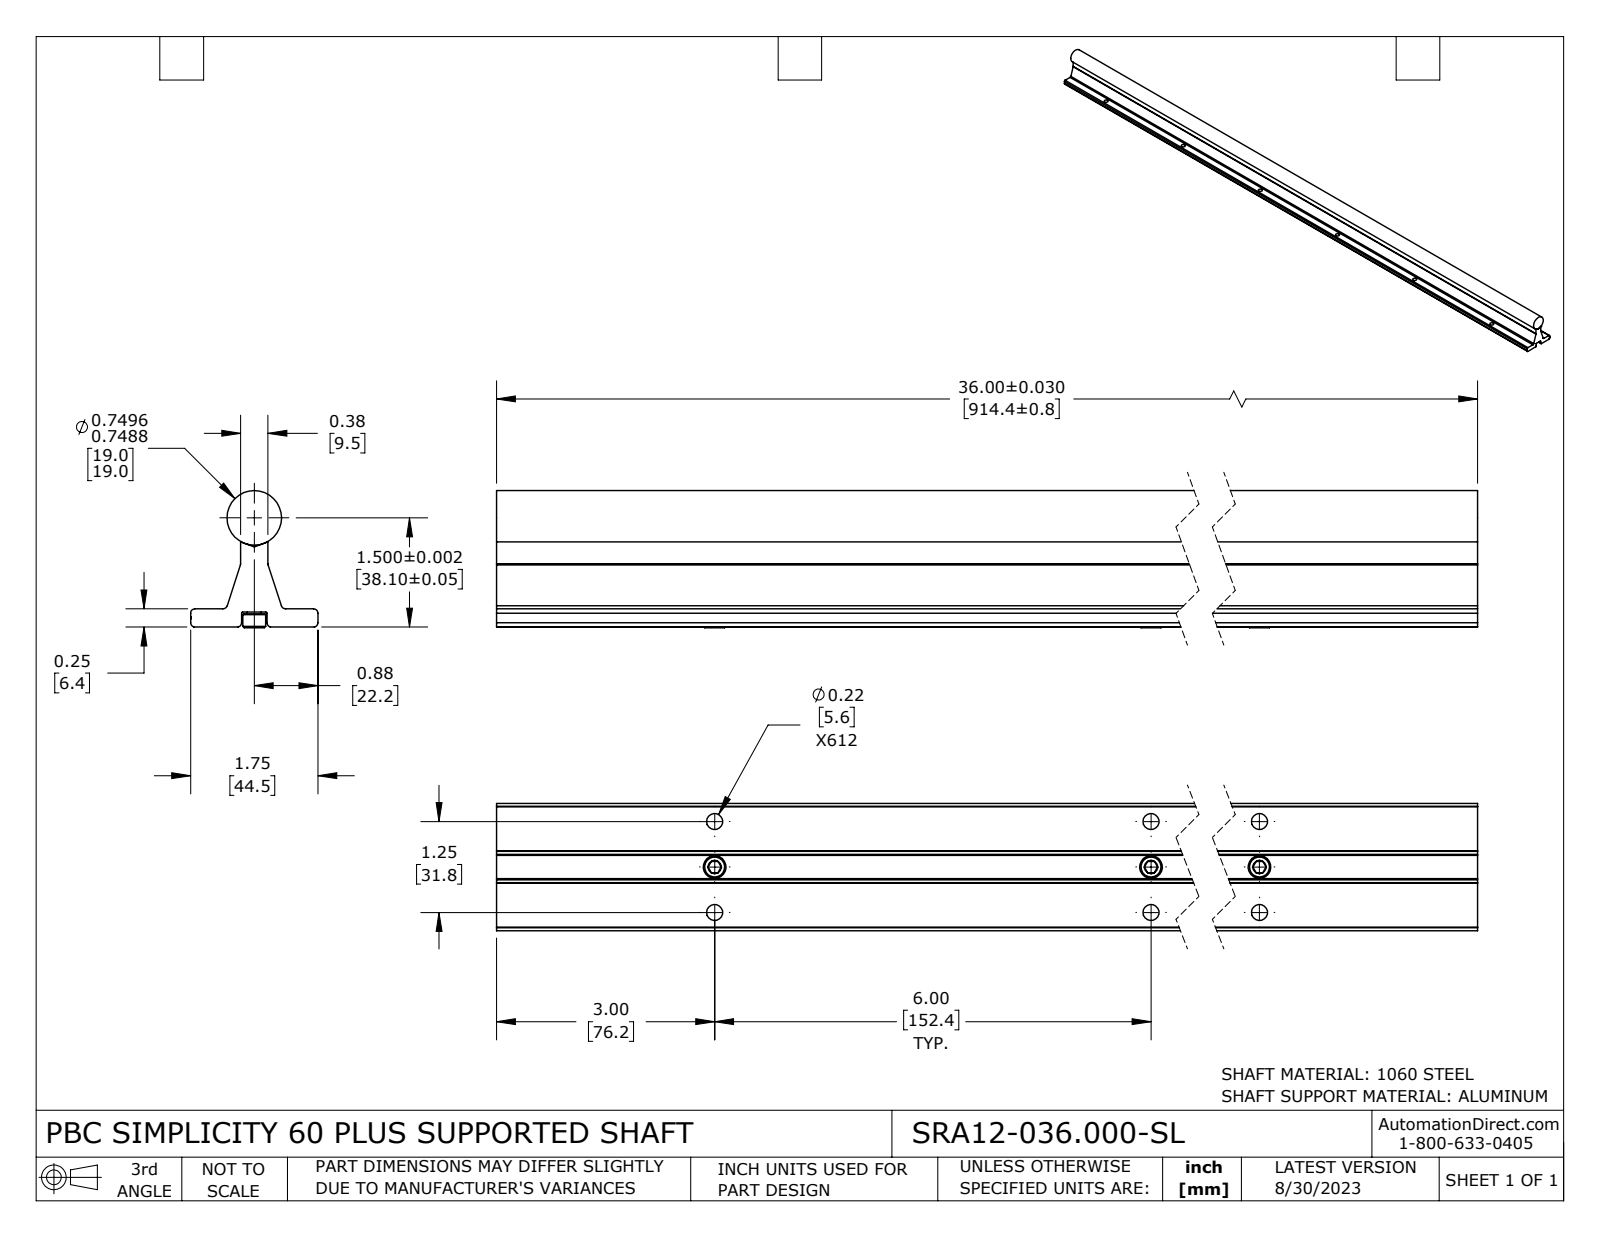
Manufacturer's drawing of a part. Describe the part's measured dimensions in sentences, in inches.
The part is named "SRA12-036.000-SL". Its 3-D file was written by "SolidWorks 2021 (CONFIG_CONTROL_DESIGN)". It is 8 solids with 281 faces: 93 planar, 98 cylindrical and 90 other. Overall it measures 36 by 1.885 by 1.75 inches. Its volume is 45.12 cubic inches and its surface area 307.8 square inches. Round holes: 18 of diameter 0.221, 6 of diameter 0.169, 6 of diameter 0.25. Round bosses or shafts: 6 of diameter 0.312, 6 of diameter 0.19, 1 of diameter 0.75. Partial cylindrical surfaces (rounded edges, fillets, slot ends): 6 of radius 0.06, 2 of radius 0.015, 2 of radius 0.062, 2 of radius 0.063. The main face-to-face distances are 0.25, 0.205, 0.045, 0.375, 0.012, 0.363, 0.688, 0.7, 1.05, 1.063. The hole center spacings are 6.033, 12.016, 6, 0.625, 12, 18.011, 6.129, 18.
